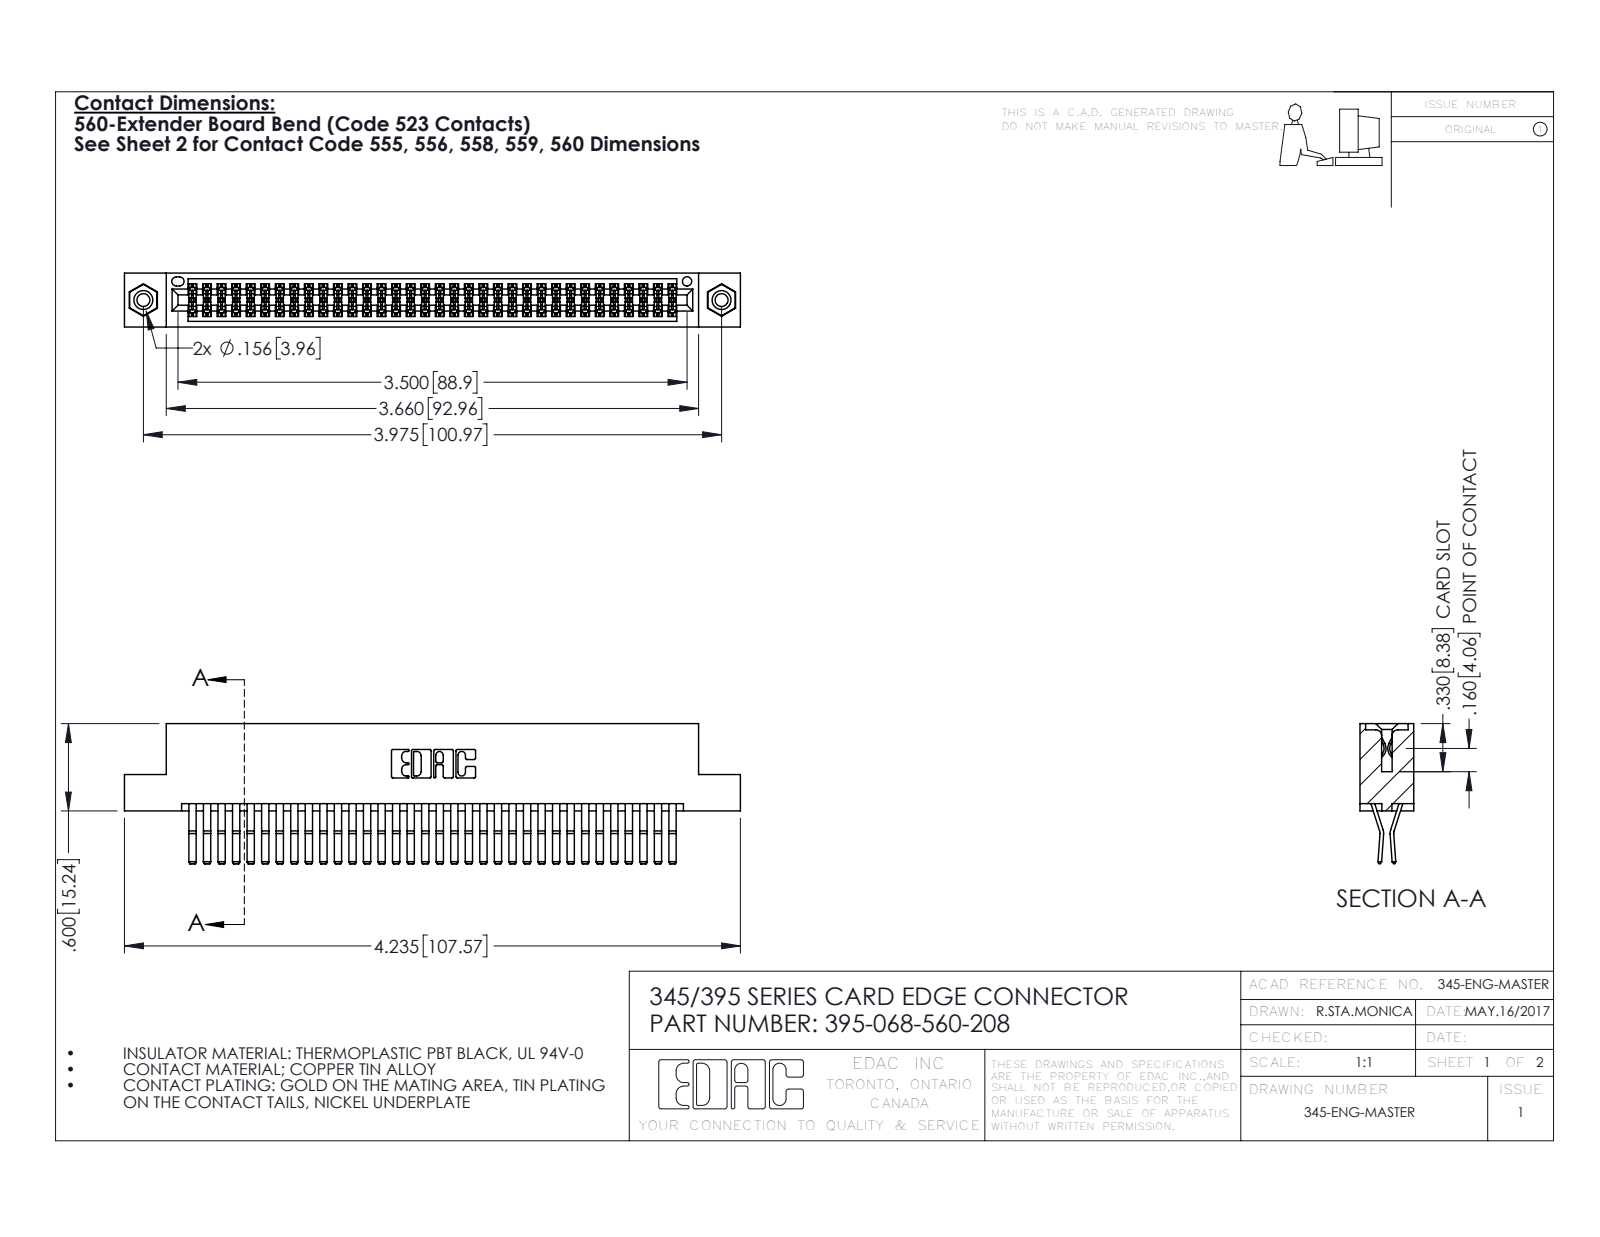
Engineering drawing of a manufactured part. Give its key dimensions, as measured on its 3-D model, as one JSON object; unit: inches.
{"part_name": "395-068-560-208; 345-250-001_345-250-003-102; 345 Part_Flush Mounting Lugs - 0.156 Dia-TI; 345-292-001_560 Tail", "step_written_by": "SolidWorks 2016 (CONFIG_CONTROL_DESIGN)", "units": "inches", "bodies": {"solids": 71, "faces": 3722, "planar": 2356, "cylindrical": 1350, "other": 16}, "overall_size": [4.235, 0.962, 0.37], "volume_in3": 0.66, "surface_area_in2": 26.33, "round_holes": [[0.089, 2], [0.125, 2], [0.156, 2], [0.064, 1]], "round_bosses_or_shafts": [[0.155, 2]], "partial_cylinders_radius": [[0.006, 102], [0.01, 22], [0.007, 6], [0.031, 6], [0.026, 3], [0.01, 2], [0.014, 2], [0.019, 2]], "face_to_face_distances": [0.025, 0.072, 0.298, 0.2, 0.37, 0.098, 0.272, 0.225, 0.175, 0.149], "hole_center_spacings": [0.27, 3.74, 3.975]}
